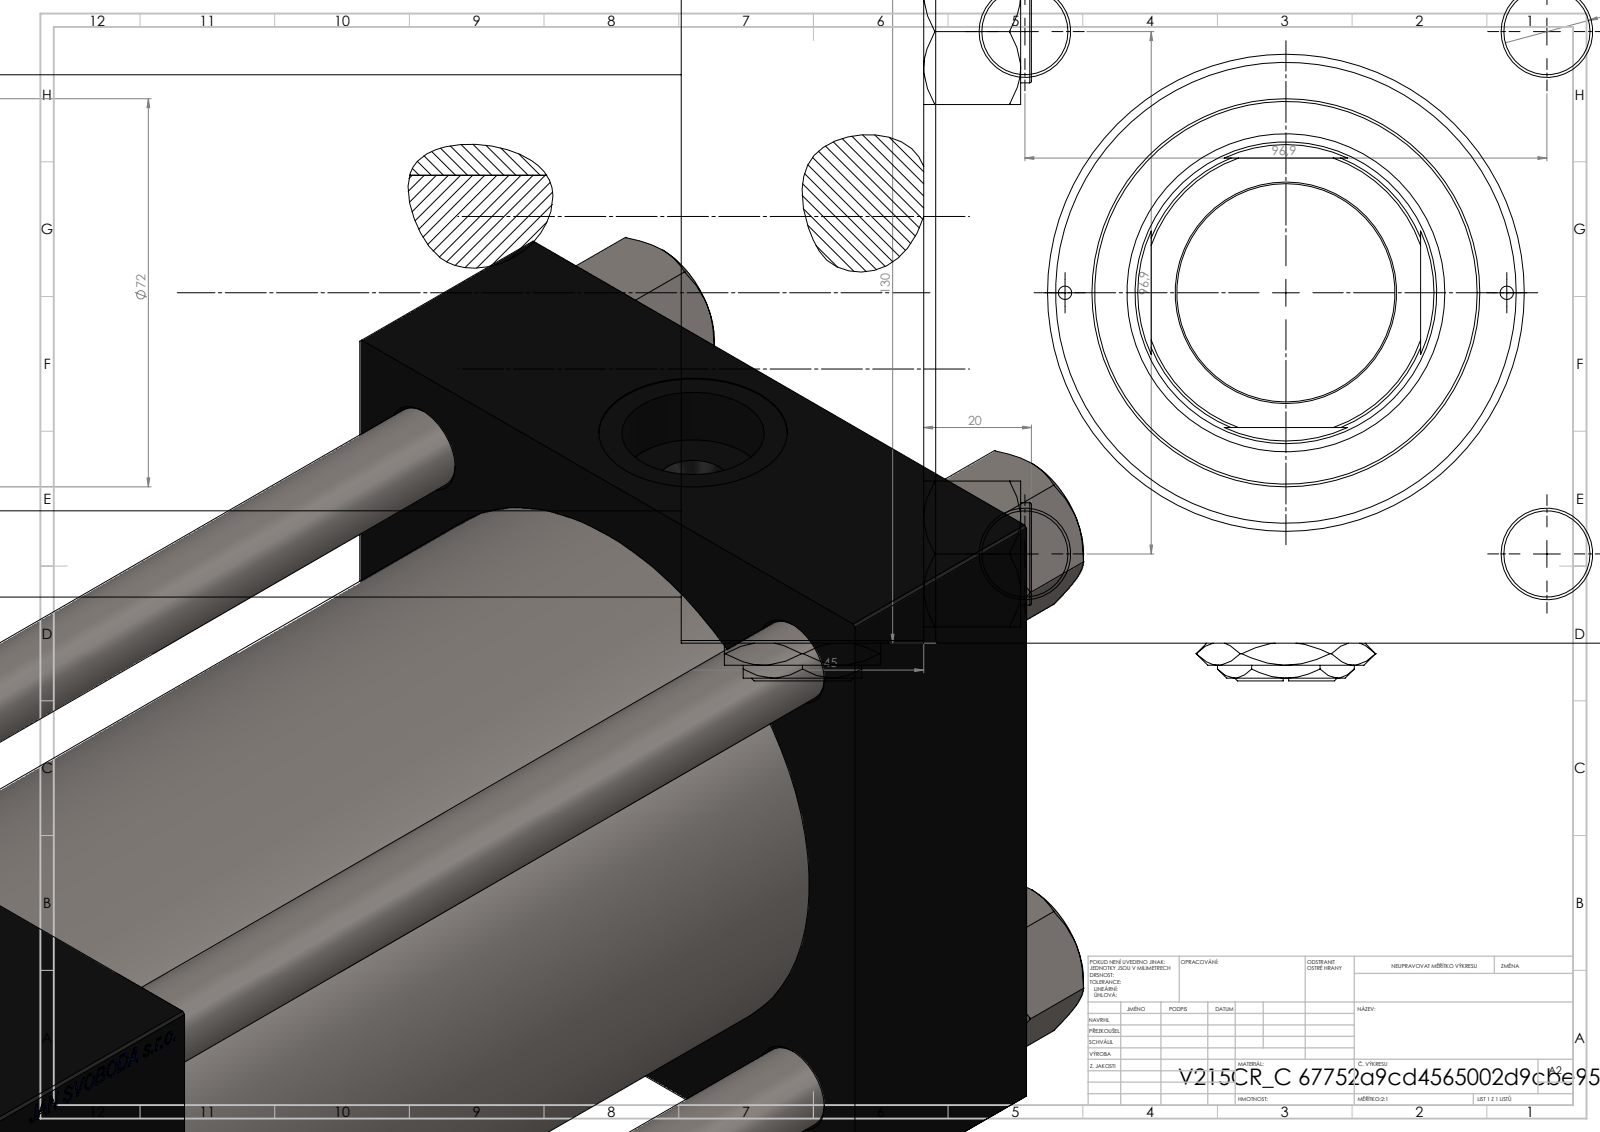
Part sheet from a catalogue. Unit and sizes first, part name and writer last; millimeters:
Units: millimetres
Overall size (bounding box): 348 × 137 × 130
Round holes (diameter × count): ⌀16 ×4, ⌀2.5 ×2, ⌀7 ×2, ⌀26.44 ×2, ⌀35 ×2, ⌀40.5 ×1, ⌀56 ×1, ⌀59 ×1, ⌀76 ×1, ⌀85.5 ×1, ⌀100 ×1
Round bosses / shafts (diameter × count): ⌀19 ×4, ⌀106 ×1, ⌀72 ×1
Partial cylindrical surfaces — rounded edges, fillets, slot ends (radius × count): R27 ×1
Main face-to-face distances: 130, 45, 293, 248, 221, 176, 72, 51, 125, 197
Hole centre spacings: 49.02, 68.52, 96.9, 101.73, 41, 137.04, 82, 223.5
Volume: 2 905 000 mm³ · Surface area: 448 200 mm²
Bodies: 13 solids, 1303 faces (623 planar, 102 cylindrical, 578 other)
Part name (STEP PRODUCT): V215CR_VCP_C; V215_VC_A; V215CR_C_Body; Zatka_pro_OIL_PORT (+2 more)
STEP written by: SolidWorks 2019 (CONFIG_CONTROL_DESIGN)
